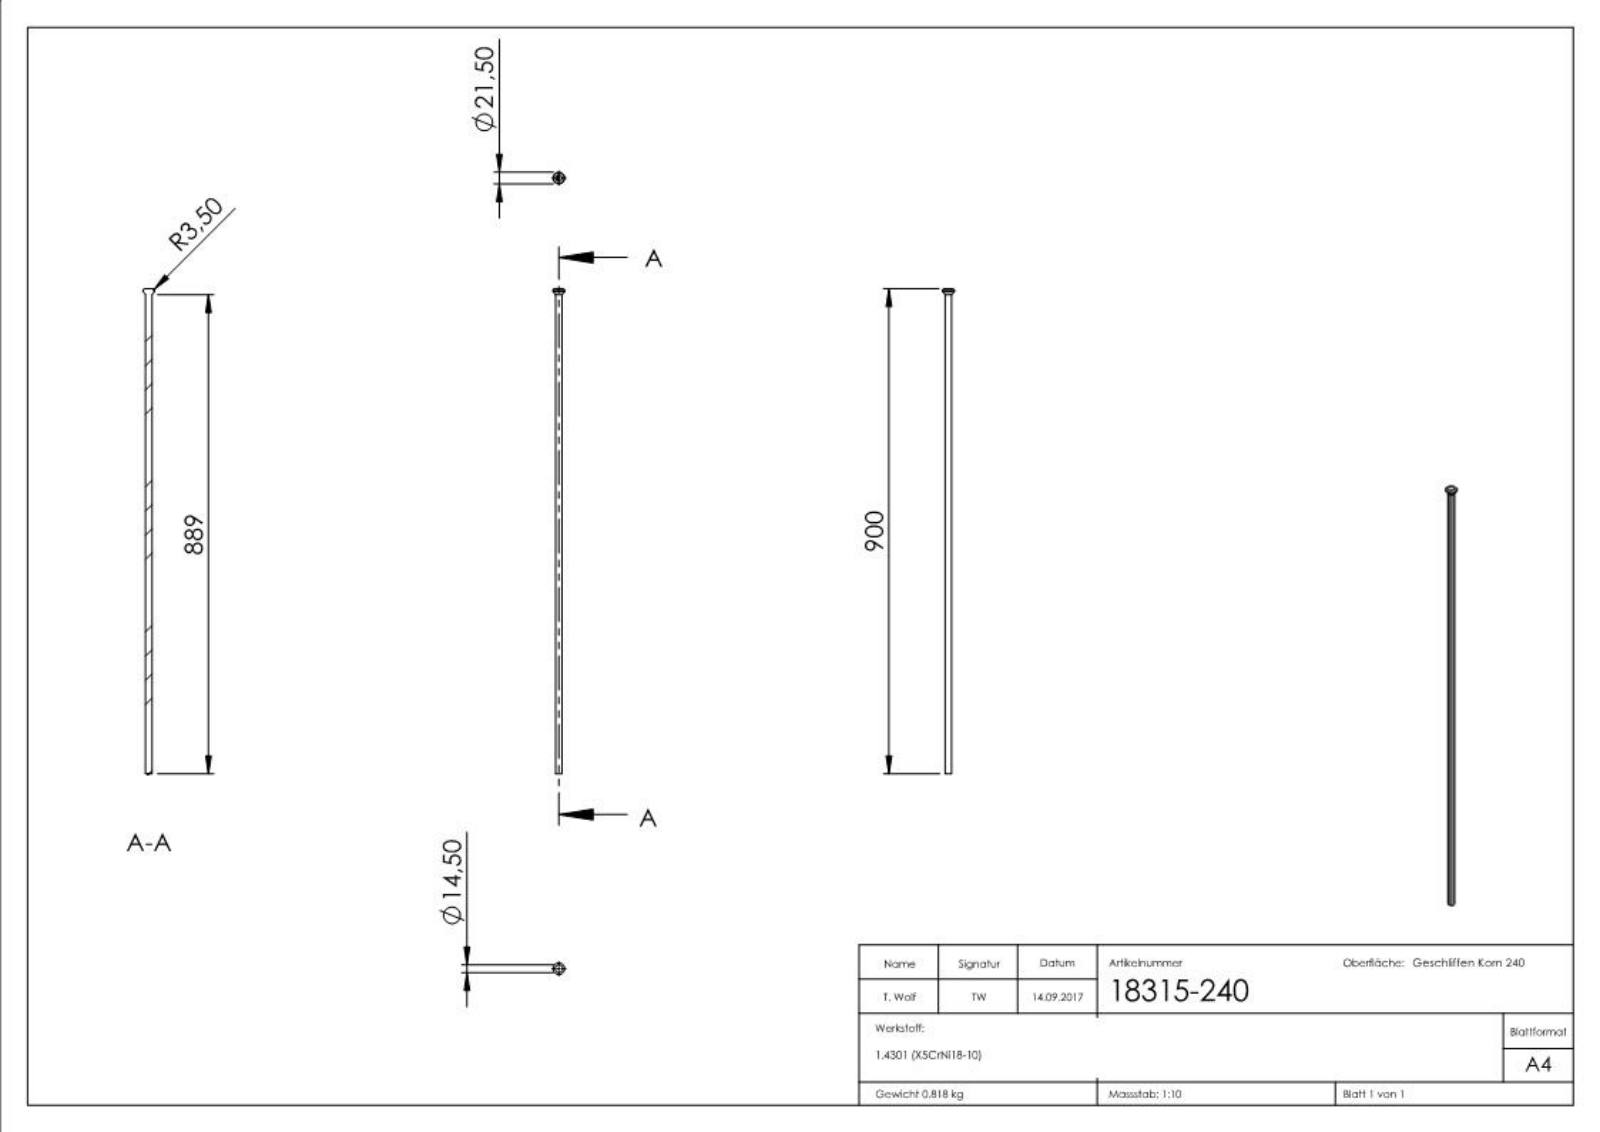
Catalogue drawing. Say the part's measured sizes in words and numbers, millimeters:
The part is named "18315-240". Its 3-D file was written by "SolidWorks 2015 (CONFIG_CONTROL_DESIGN)". It is 1 solid with 236 faces: 124 planar, 4 cylindrical and 108 other. Overall it measures 900 by 21.5 by 21.5 millimeters. Its volume is 103 539 cubic millimeters and its surface area 34 645 square millimeters. Round bosses or shafts: 1 of diameter 21.5, 1 of diameter 12. The main face-to-face distances are 900, 0.5, 899.5, 0.99, 1.83, 1.78, 0.83, 2.05, 1.98, 1.91.
